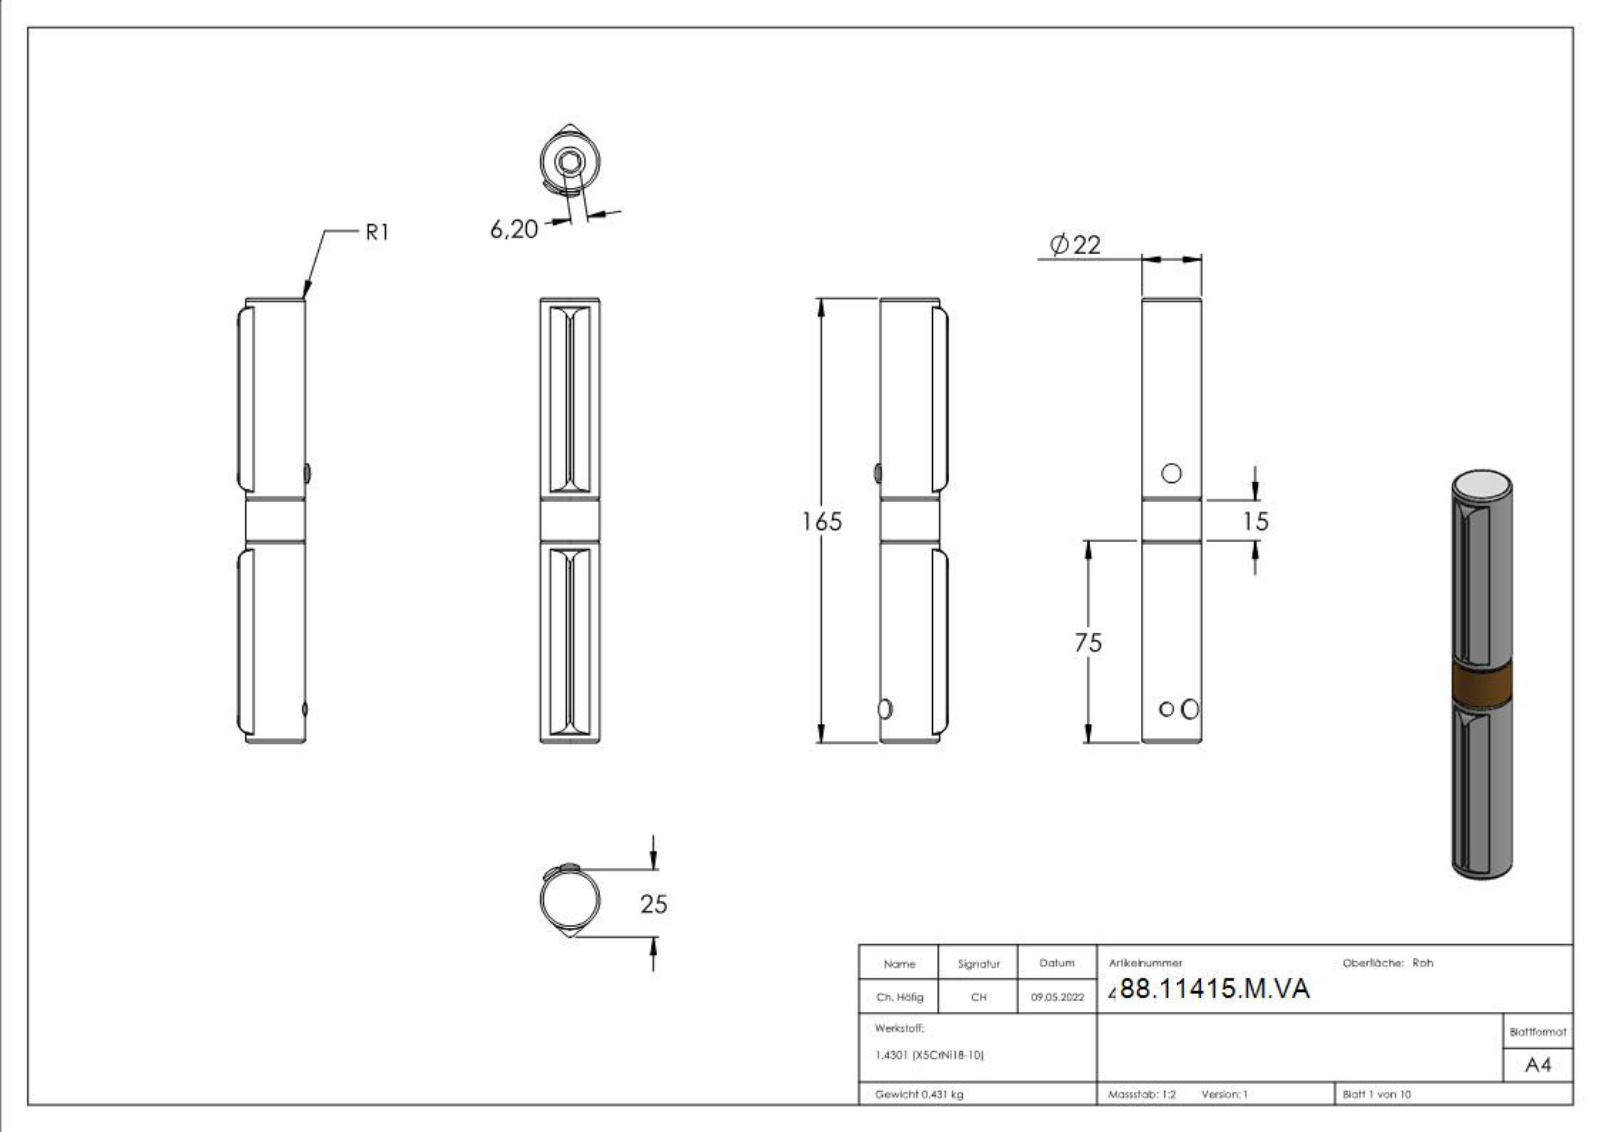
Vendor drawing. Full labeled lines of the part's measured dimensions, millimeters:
Part name (STEP PRODUCT): 415-M-VA Teil7_415-M-VA Teil7; 415-M-VA Teil5_415-M-VA Teil5; 415-M-VA Teil8_415-M-VA Teil8; 415-M-VA Teil1_415-M-VA Teil1 (+5 more)
STEP written by: SolidWorks 2018 (CONFIG_CONTROL_DESIGN)
Units: millimetres
Bodies: 9 solids, 304 faces (185 planar, 39 cylindrical, 80 other)
Overall size (bounding box): 165 × 27 × 22
Volume: 54 728 mm³ · Surface area: 49 973 mm²
Round holes (diameter × count): ⌀4.5 ×3, ⌀5 ×3, ⌀4.2 ×1, ⌀4.3 ×1, ⌀11.2 ×1, ⌀15 ×1, ⌀18.4 ×1, ⌀18.5 ×1
Round bosses / shafts (diameter × count): ⌀7 ×2, ⌀4 ×2, ⌀3.8 ×2, ⌀22 ×1, ⌀18.3 ×1, ⌀18 ×1, ⌀14.5 ×1, ⌀5.4 ×1
Partial cylindrical surfaces — rounded edges, fillets, slot ends (radius × count): R2 ×2, R14 ×1
Main face-to-face distances: 161, 4, 90, 157, 75, 71, 86, 165, 14, 18
Hole centre spacings: 4.6, 5.8, 7.95
